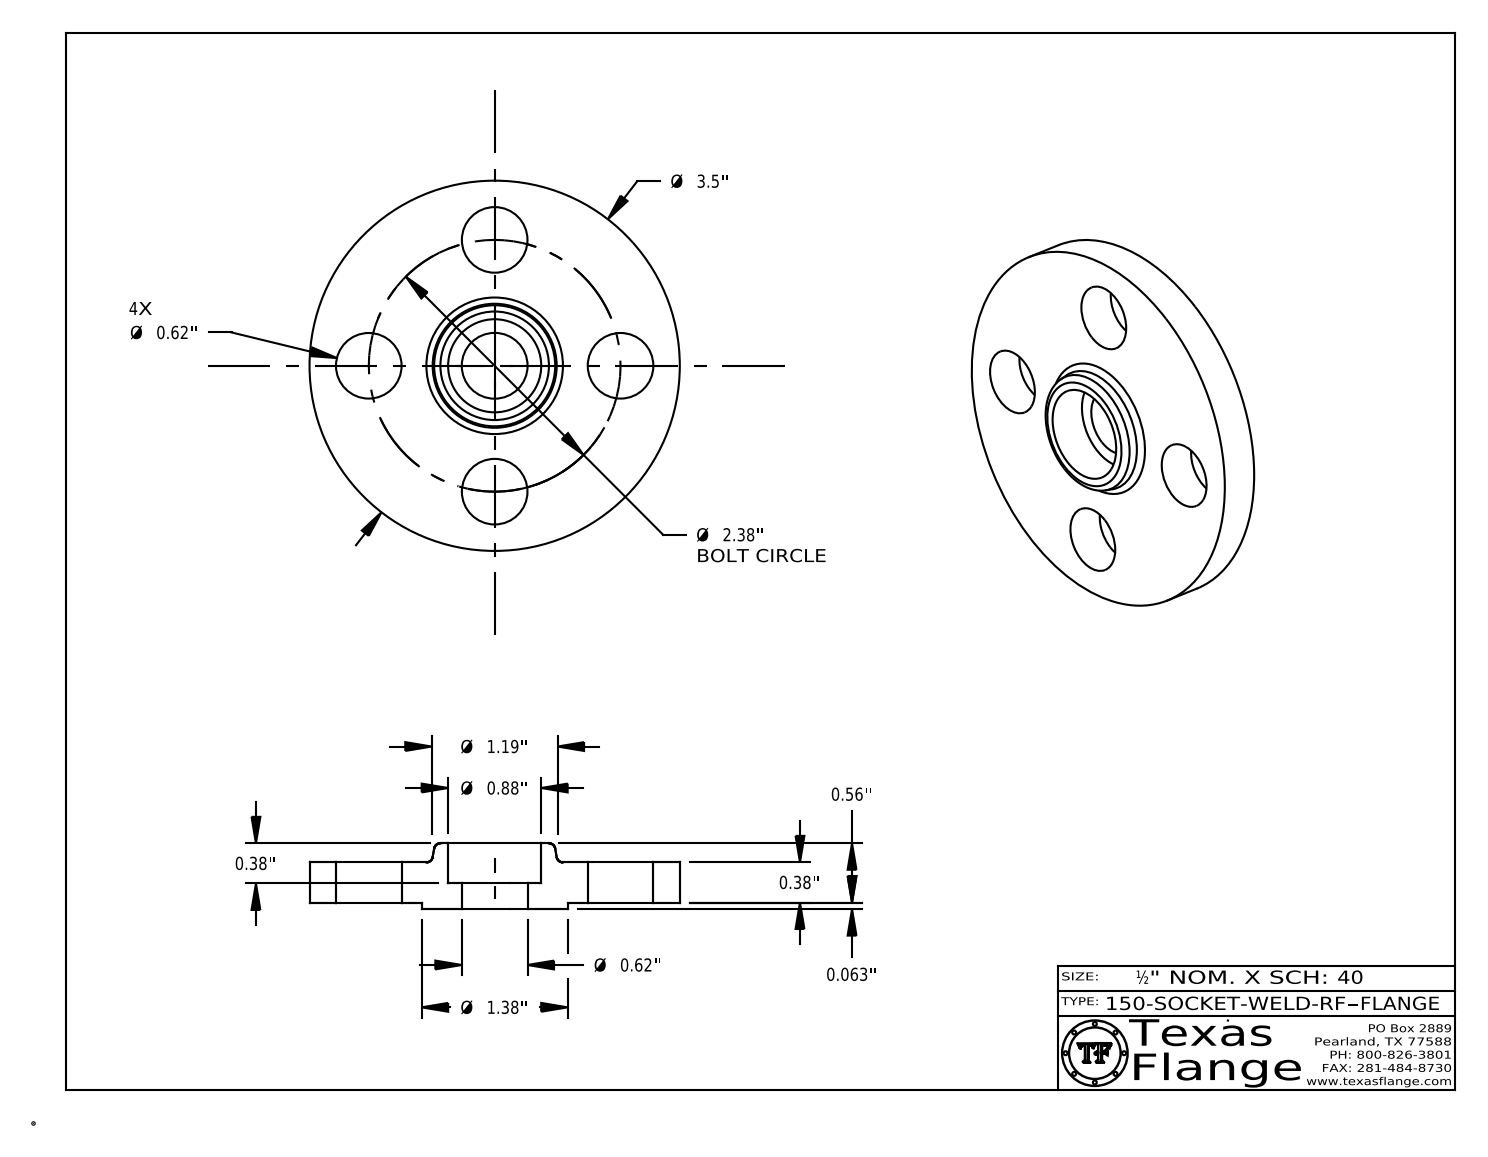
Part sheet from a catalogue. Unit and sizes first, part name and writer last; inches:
Units: inches
Overall size (bounding box): 3.5 × 3.5 × 0.623
Round holes (diameter × count): ⌀0.62 ×4, ⌀0.495 ×1, ⌀0.622 ×1, ⌀0.88 ×1
Round bosses / shafts (diameter × count): ⌀0.03 ×8, ⌀3.5 ×1, ⌀1.38 ×1, ⌀0.39 ×1
Main face-to-face distances: 0.38, 0.063, 0.443, 0.18, 0.243, 0.2, 0.622, 0.56, 0.428, 0.365
Hole centre spacings: 1.19, 1.683, 0.911, 2.199, 2.38, 1.19
Volume: 3.174 in³ · Surface area: 25.67 in²
Bodies: 1 solid, 412 faces (370 planar, 36 cylindrical, 6 other)
Part name (STEP PRODUCT): 150-SOCKET-WELD-RF
STEP written by: CATIA V5 STEP AP214 (AUTOMOTIVE_DESIGN)
